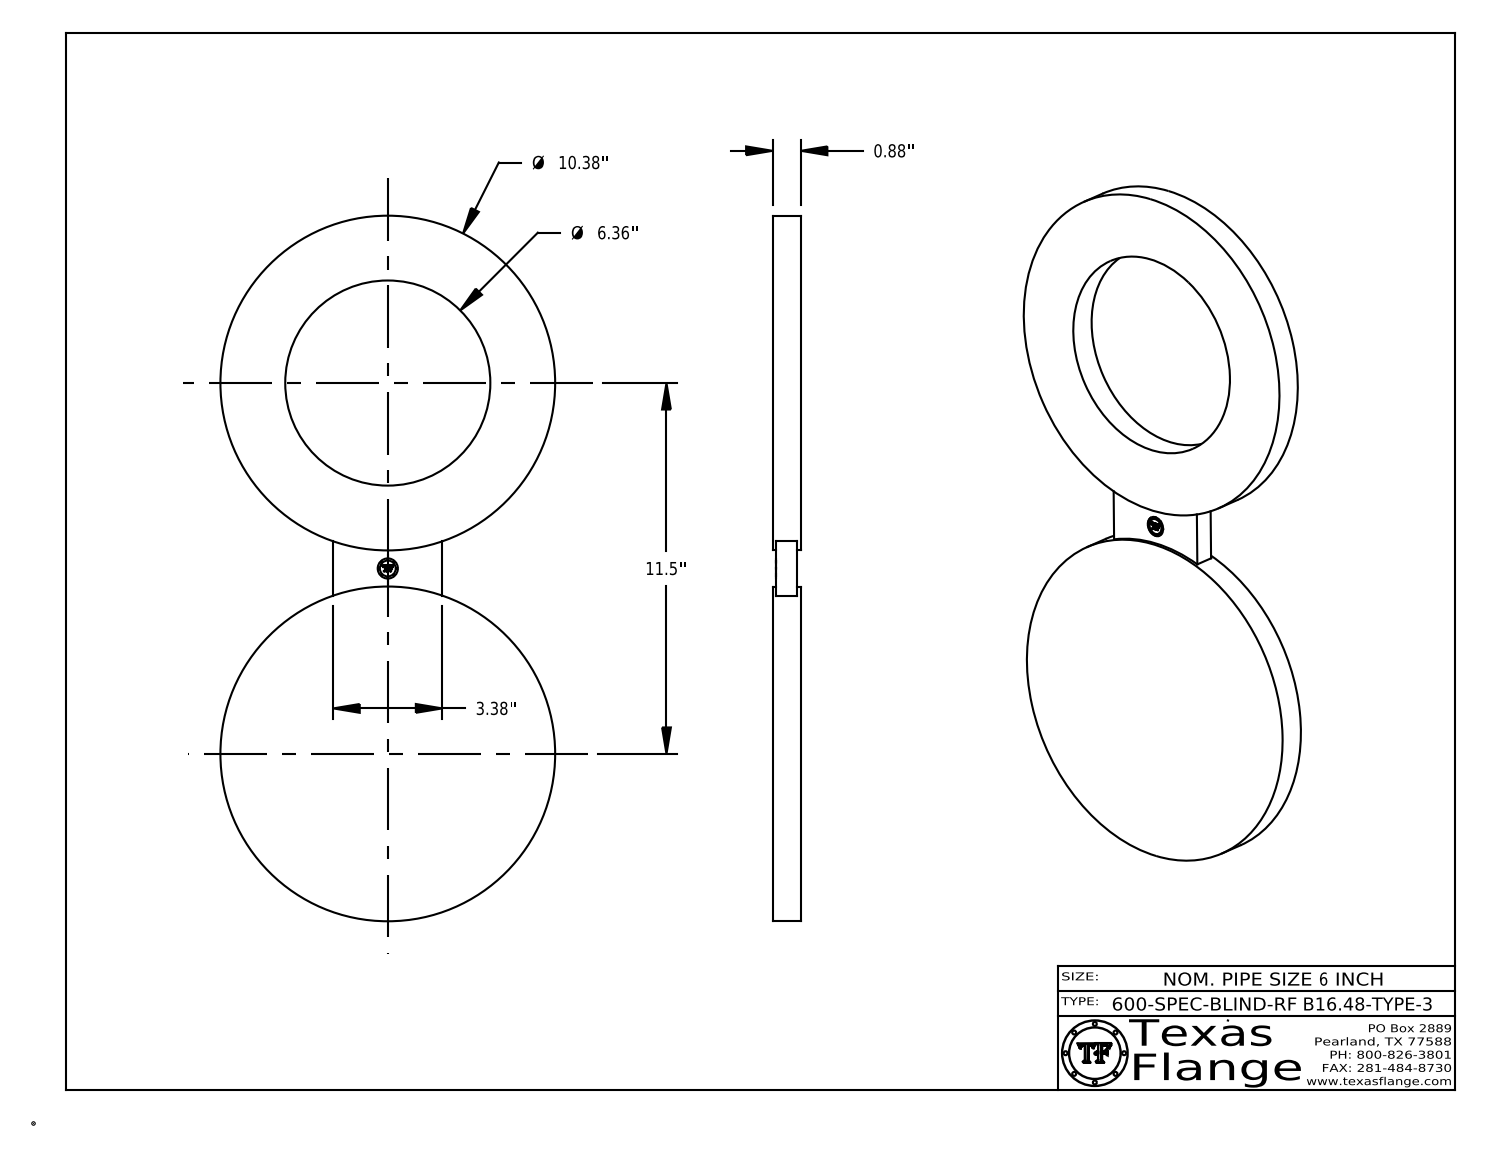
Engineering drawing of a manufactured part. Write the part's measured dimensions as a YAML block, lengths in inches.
part_name: "6-600-SPEC-BLIND-RF-B16.48-TYPE-3"
step_written_by: "CATIA V5 STEP AP214 (AUTOMOTIVE_DESIGN)"
units: inches
bodies: {solids: 1, faces: 399, planar: 373, cylindrical: 26, other: 0}
overall_size: [21.88, 10.38, 0.88]
volume: 123.9
surface_area: 356.6
round_holes:
  - {diameter: 0.625, count: 1}
  - {diameter: 6.36, count: 1}
round_bosses_or_shafts:
  - {diameter: 0.038, count: 8}
  - {diameter: 10.38, count: 2}
  - {diameter: 0.492, count: 1}
face_to_face_distances: [0.88, 0.11, 0.77, 0.66, 3.38, 0.125, 0.755, 0.645, 0.015, 1.628]
hole_center_spacings: [5.75]
